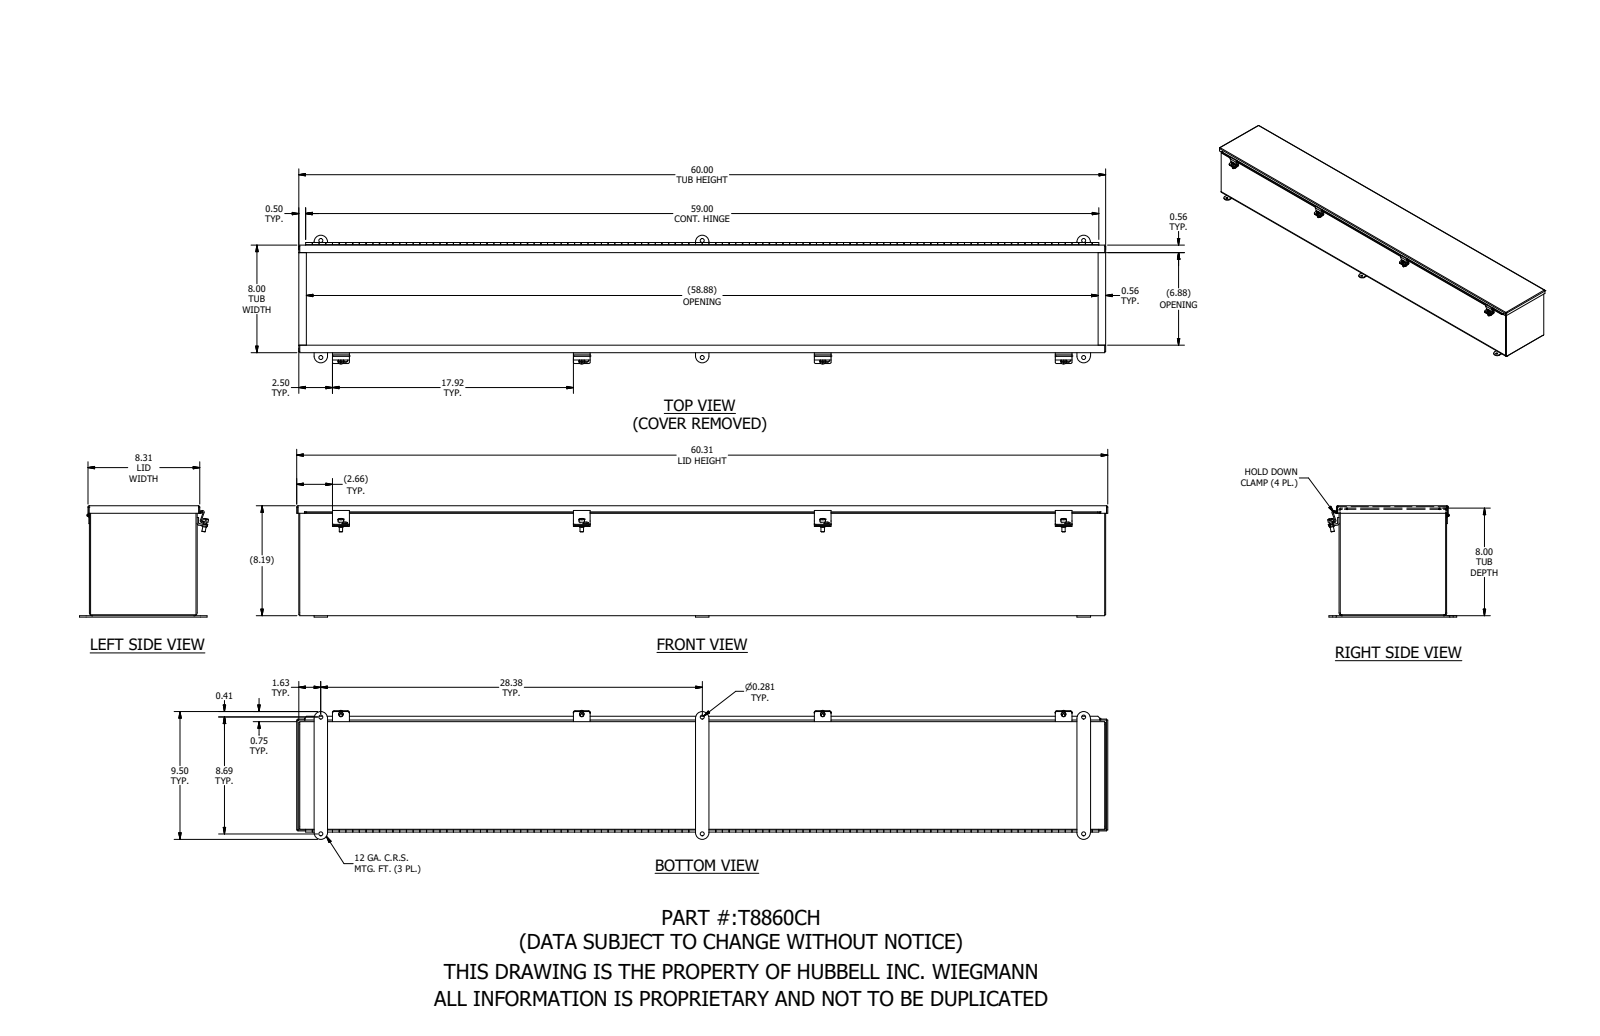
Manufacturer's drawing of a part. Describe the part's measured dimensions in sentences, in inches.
The part is named "T8860CH". Its 3-D file was written by "SolidWorks 2021 (AUTOMOTIVE_DESIGN)". It is 22 solids with 1221 faces: 592 planar, 601 cylindrical and 28 other. Overall it measures 60.313 by 9.595 by 8.283 inches. Its volume is 169.3 cubic inches and its surface area 4 686 square inches. Round holes: 6 of diameter 0.281, 4 of diameter 0.196, 1 of diameter 0.116. Round bosses or shafts: 4 of diameter 0.41, 4 of diameter 0.344, 4 of diameter 0.25, 1 of diameter 0.2, 1 of diameter 0.1. Partial cylindrical surfaces (rounded edges, fillets, slot ends): 16 of radius 0.125, 9 of radius 0.031, 9 of radius 0.105, 8 of radius 0.133, 6 of radius 0.5, 3 of radius 0.063, 3 of radius 0.126, 2 of radius 0.156. The main face-to-face distances are 0.074, 7.926, 8.115, 8, 7.852, 8.189, 8.041, 59.926, 0.189, 0.116. The hole center spacings are 8.687, 17.917, 28.375, 28.375, 29.675, 29.675, 56.75, 57.411.
